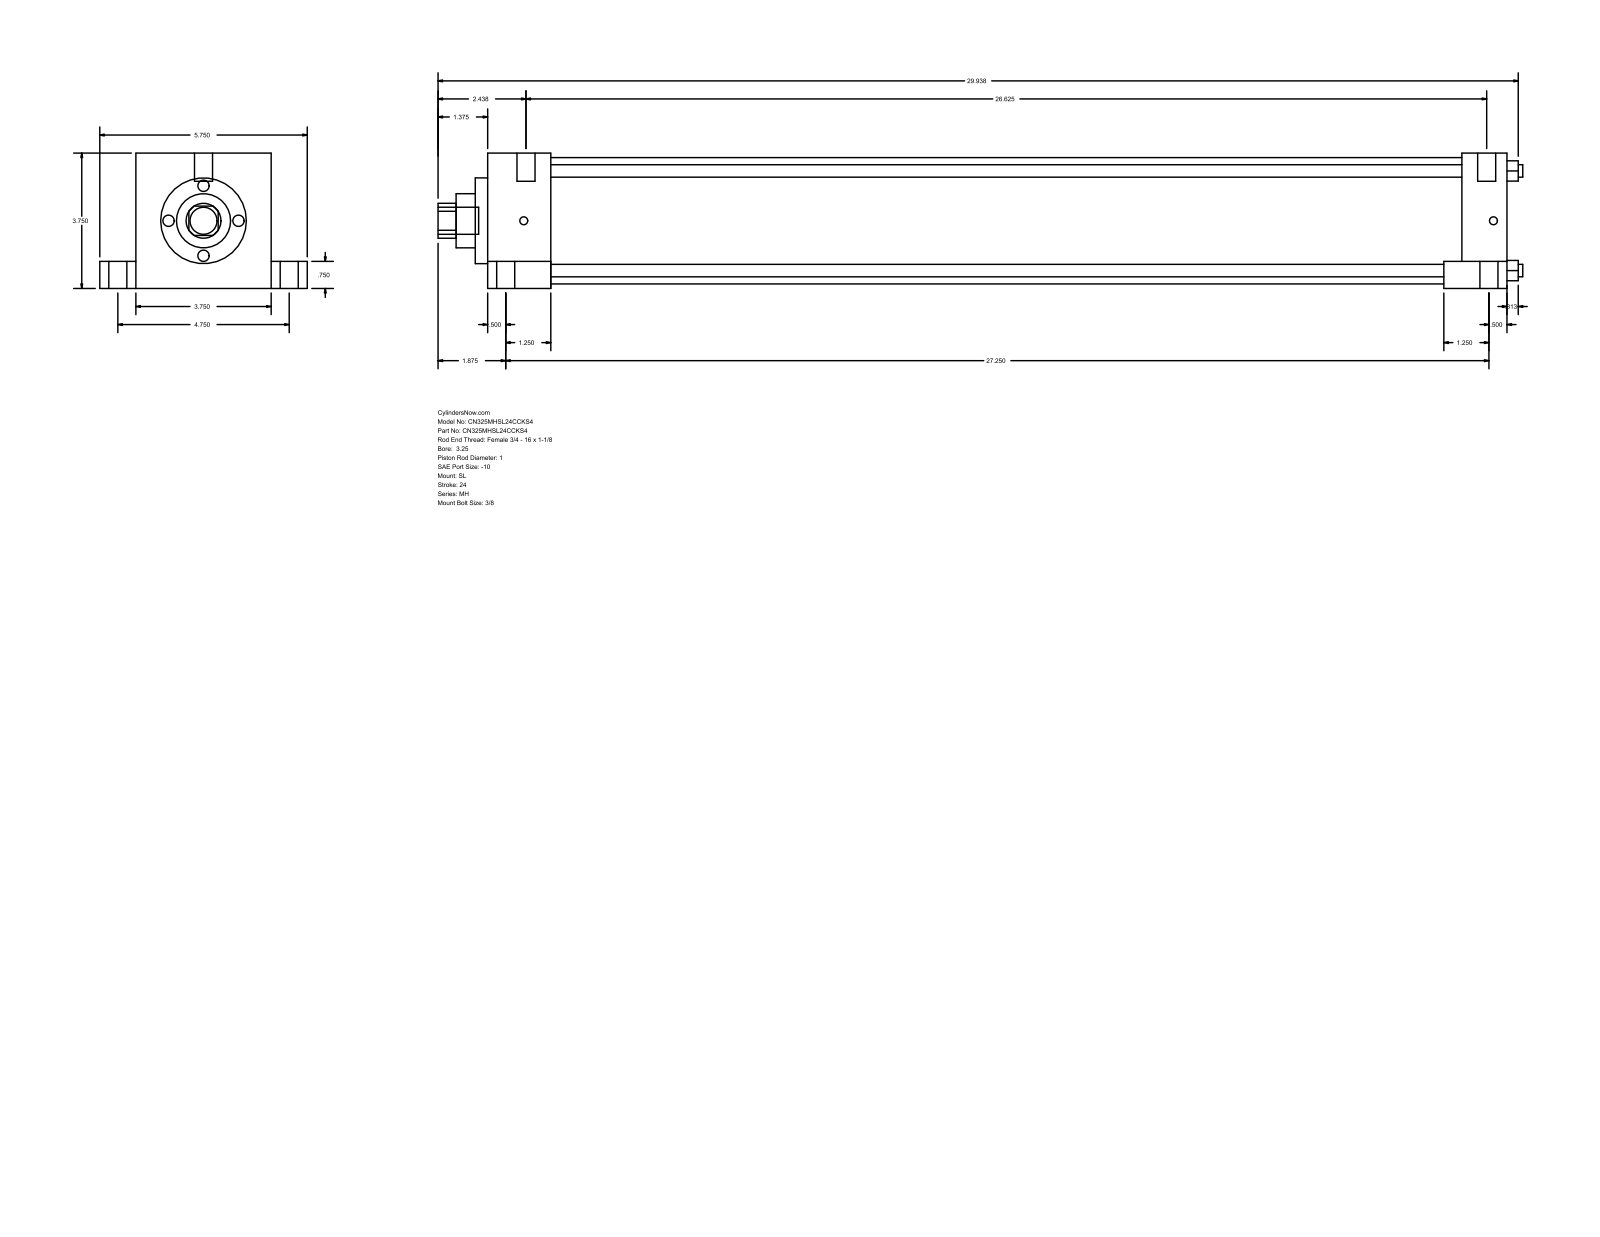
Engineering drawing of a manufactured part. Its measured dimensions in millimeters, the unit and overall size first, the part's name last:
Units: millimetres
Overall size (bounding box): 763.59 × 146.05 × 95.25
Round holes (diameter × count): ⌀8.76 ×4, ⌀25.4 ×1, ⌀38.1 ×1, ⌀60.33 ×1, ⌀88.9 ×1
Round bosses / shafts (diameter × count): ⌀12.7 ×6, ⌀19.05 ×5, ⌀5.56 ×4
Partial cylindrical surfaces — rounded edges, fillets, slot ends (radius × count): R12.29 ×1
Main face-to-face distances: 95.24, 717.56, 44.46, 673.1, 25.41, 120.65, 19.05, 76.19, 685.81, 641.35
Hole centre spacings: 49.57, 70.1, 99.14
Bodies: 0 solids, 110 faces (77 planar, 33 cylindrical, 0 other)
Part name (STEP PRODUCT): MH_SL__0325_1
STEP written by: GSSL Pune (CONFIG_CONTROL_DESIGN)
